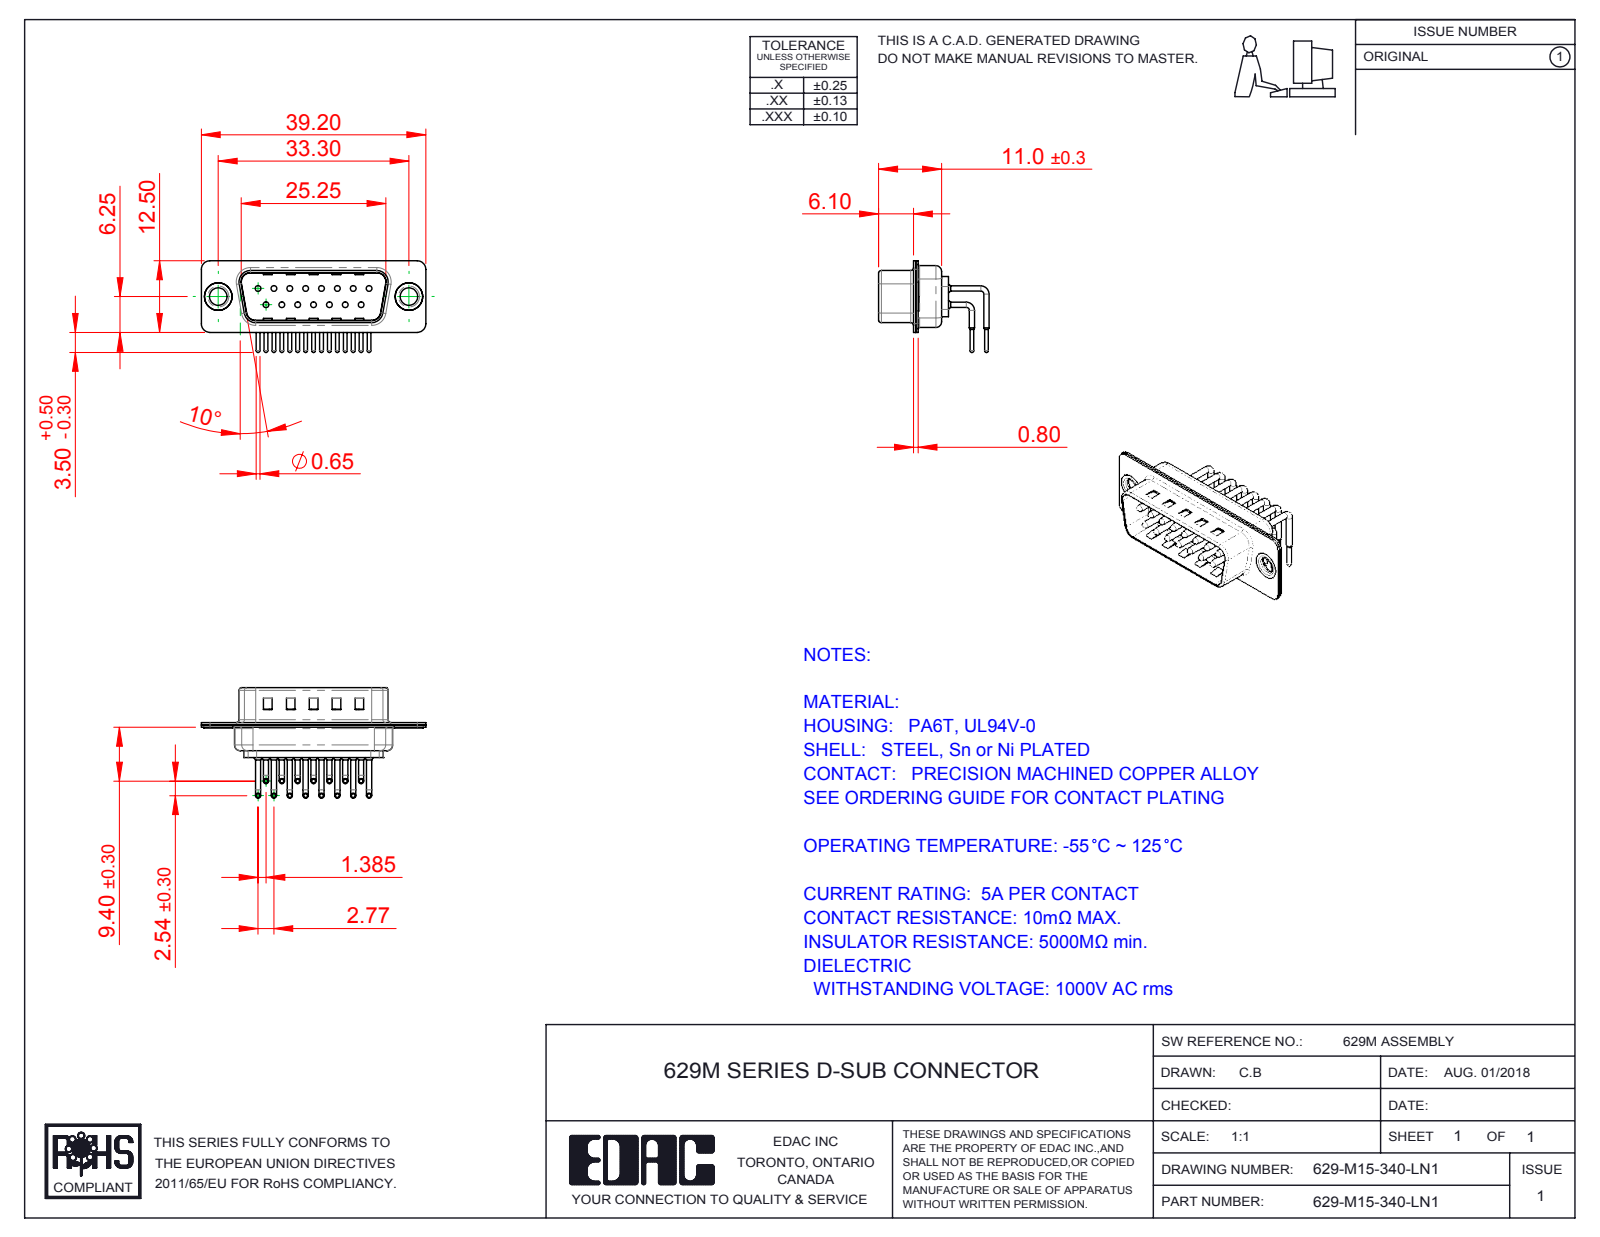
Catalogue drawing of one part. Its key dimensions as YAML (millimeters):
part_name: "629-M15-340-LN1; 629M Contact Row 2; 629M Contact Row 1; 629M Shell Rear_15 Contacts (+3 more)"
step_written_by: "SolidWorks 2016 (CONFIG_CONTROL_DESIGN)"
units: millimeters
bodies: {solids: 20, faces: 1964, planar: 1099, cylindrical: 657, other: 208}
overall_size: [39.2, 19.29, 16]
volume: 1881
surface_area: 5213
round_holes:
  - {diameter: 1, count: 15}
  - {diameter: 1.7, count: 15}
  - {diameter: 2, count: 15}
  - {diameter: 3.05, count: 2}
  - {diameter: 4, count: 2}
  - {diameter: 4.8, count: 2}
round_bosses_or_shafts:
  - {diameter: 0.9, count: 30}
  - {diameter: 1.5, count: 15}
  - {diameter: 0.65, count: 15}
  - {diameter: 5, count: 2}
  - {diameter: 4.9, count: 2}
  - {diameter: 3.55, count: 2}
partial_cylinders:
  - {radius: 1.5, count: 16}
  - {radius: 1.01, count: 15}
  - {radius: 2, count: 12}
  - {radius: 0.5, count: 8}
  - {radius: 1.6, count: 8}
  - {radius: 0.25, count: 4}
  - {radius: 0.6, count: 4}
  - {radius: 0.65, count: 4}
face_to_face_distances: [0.4, 0.85, 9.55, 8.7, 1.25, 0.8, 10.4, 1.5, 0.35, 1.9]
hole_center_spacings: [3.16, 2.77, 5.54, 8.31, 11.08, 5.03, 5.04, 7.48]
